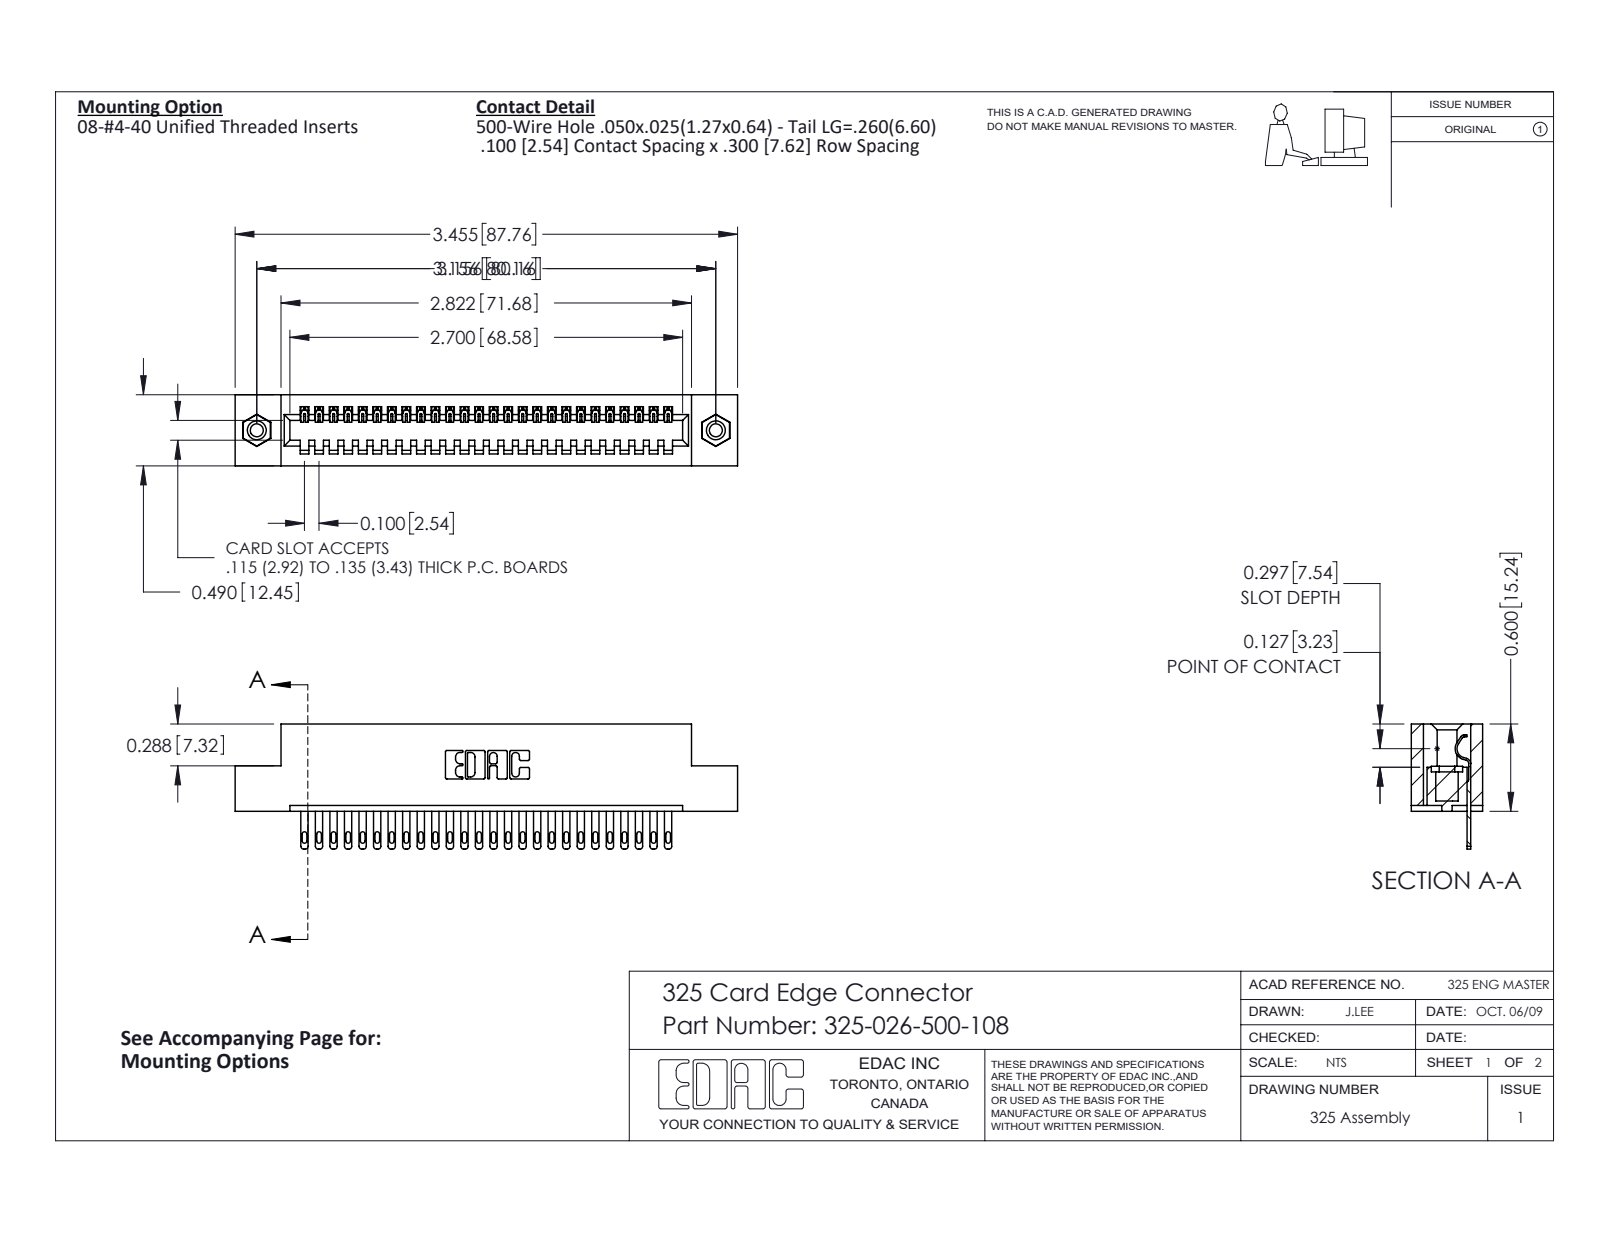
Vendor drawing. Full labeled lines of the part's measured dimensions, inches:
Part name (STEP PRODUCT): 325 Part_TI; 325-292-001_325-293-100; 325-026-500-108; 345-250-001_345-250-003-102
STEP written by: SolidWorks 2016 (CONFIG_CONTROL_DESIGN)
Units: inches
Bodies: 29 solids, 1578 faces (1038 planar, 524 cylindrical, 16 other)
Overall size (bounding box): 3.455 × 0.86 × 0.49
Volume: 0.673 in³ · Surface area: 18.37 in²
Round holes (diameter × count): ⌀0.089 ×2, ⌀0.125 ×2, ⌀0.16 ×2
Round bosses / shafts (diameter × count): ⌀0.155 ×2
Partial cylindrical surfaces — rounded edges, fillets, slot ends (radius × count): R0.006 ×52, R0.016 ×52, R0.02 ×52, R0.01 ×22, R0.007 ×6, R0.031 ×6, R0.026 ×3, R0.014 ×1
Main face-to-face distances: 0.083, 0.407, 0.49, 0.3, 0.107, 0.383, 0.025, 0.325, 0.04, 0.6
Hole centre spacings: 3.156
